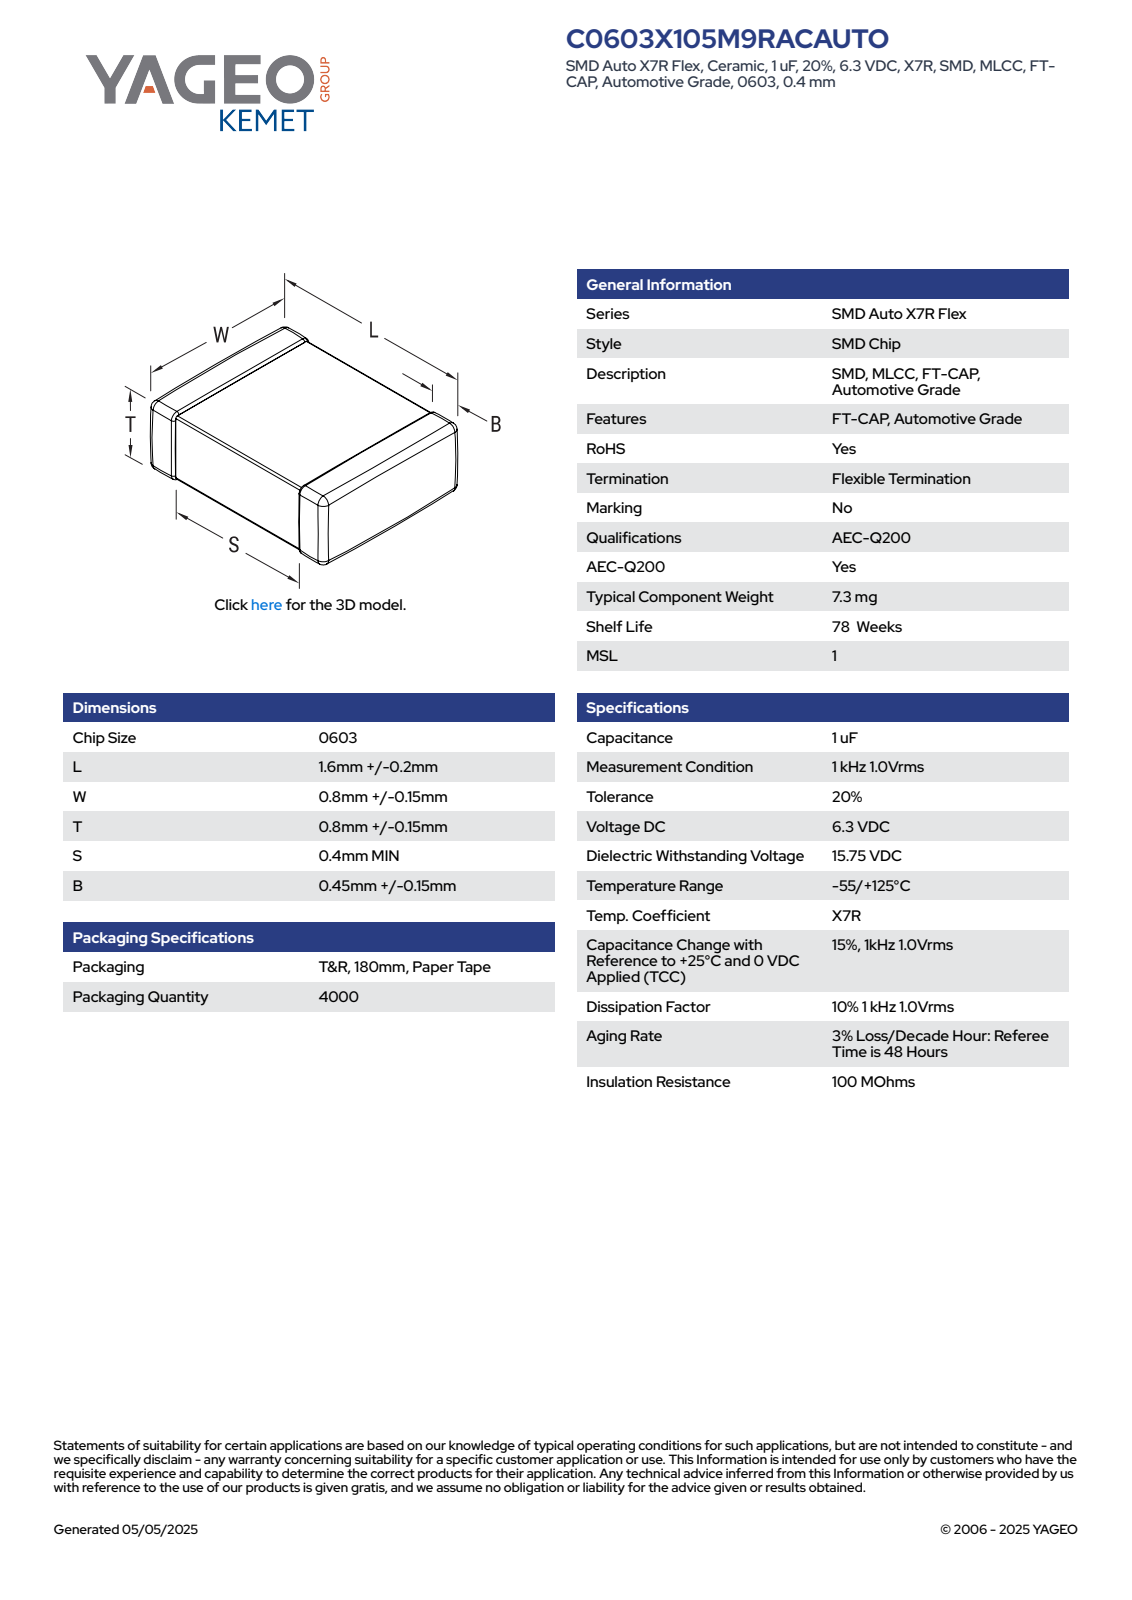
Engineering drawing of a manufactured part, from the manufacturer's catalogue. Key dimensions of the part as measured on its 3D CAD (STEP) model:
Part name (STEP PRODUCT): CCS_CCSTD_0603_L1.8W0.95T0.95B0.45
STEP written by: SolidWorks 2021 (AUTOMOTIVE_DESIGN)
Units: millimetres
Bodies: 4 solids, 121 faces (71 planar, 34 cylindrical, 16 other)
Overall size (bounding box): 1.8 × 0.95 × 0.95
Volume: 2 mm³ · Surface area: 9 mm²
Main face-to-face distances: 0.93, 0.95, 0.91, 1.8, 0.92, 0.94, 0.83, 0.97, 0.38, 0.57
